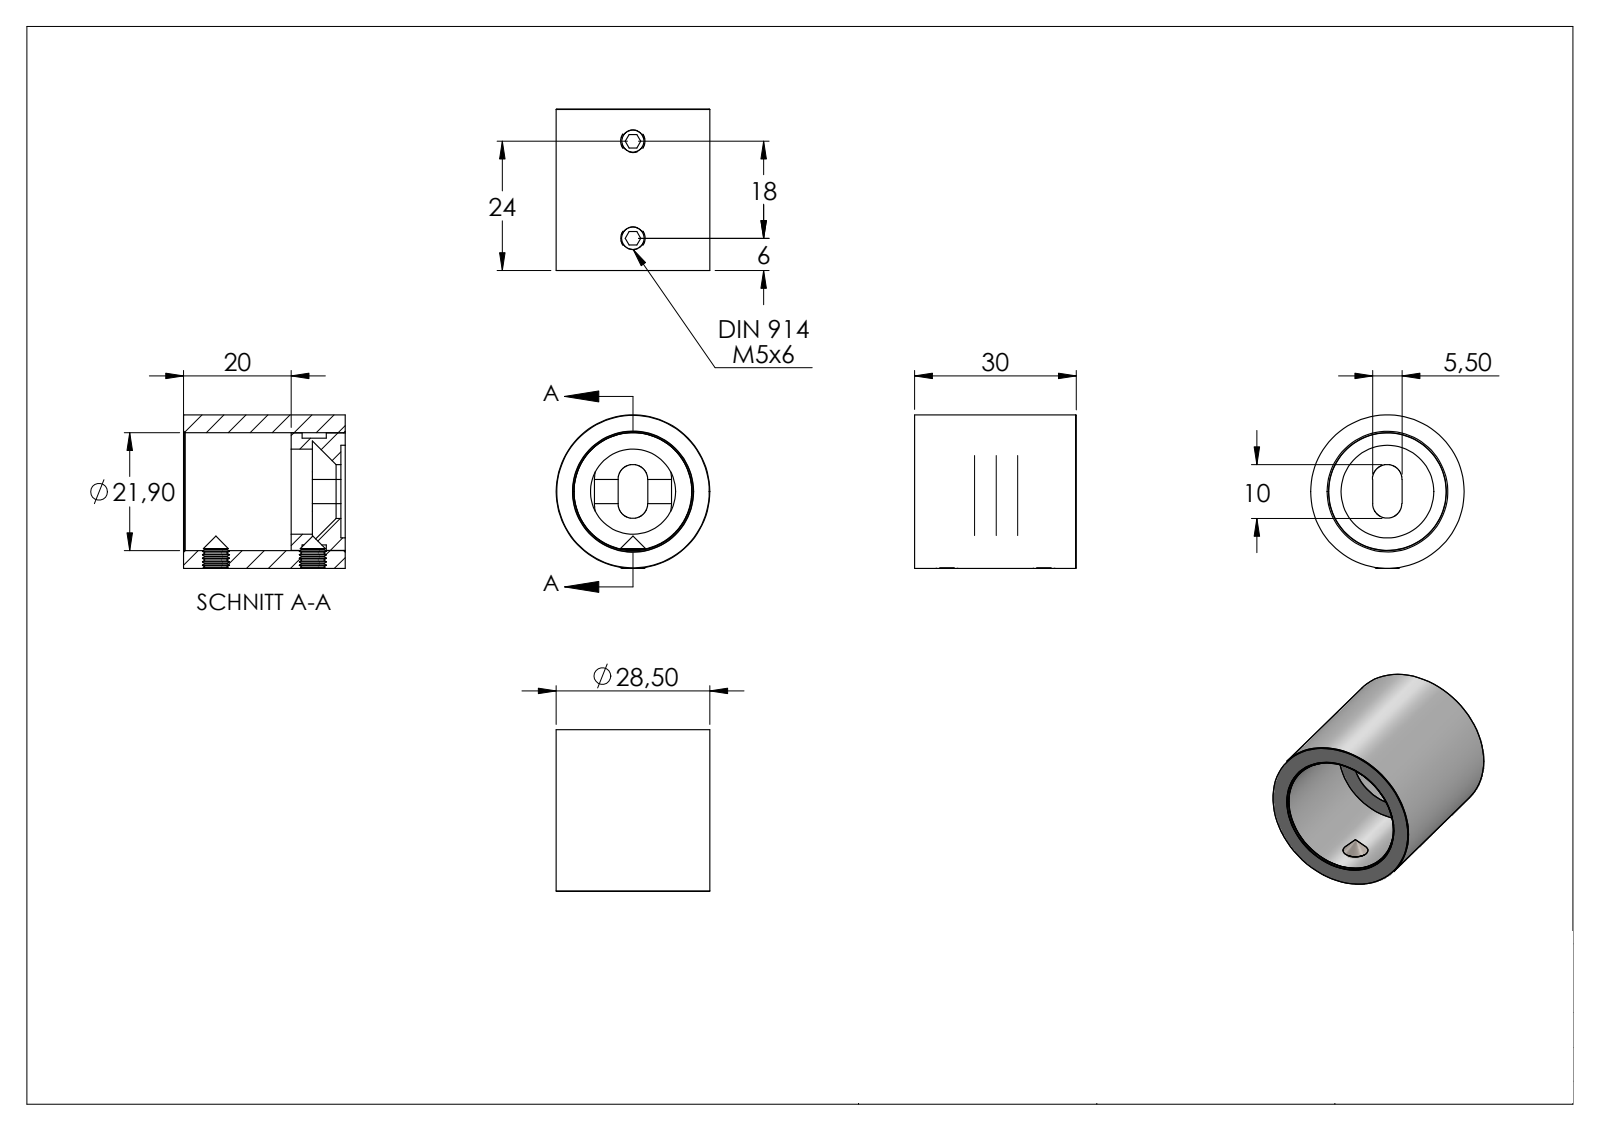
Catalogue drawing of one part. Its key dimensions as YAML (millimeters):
part_name: "54180-240-XX Teil1; 54180-240-XX Teil1_54180-V4A-21 Teil1; 54180-240-XX Teil2; 54180-240-XX Teil2_54180-V4A-21 Teil2 (+3 more)"
step_written_by: "SolidWorks 2018 (CONFIG_CONTROL_DESIGN)"
units: millimeters
bodies: {solids: 4, faces: 379, planar: 185, cylindrical: 51, other: 143}
overall_size: [30, 28.5, 28.5]
volume: 9741
surface_area: 7443
round_holes:
  - {diameter: 4.2, count: 2}
  - {diameter: 15.8, count: 1}
  - {diameter: 17.2, count: 1}
  - {diameter: 21.9, count: 1}
round_bosses_or_shafts:
  - {diameter: 5, count: 2}
  - {diameter: 28.5, count: 1}
  - {diameter: 21.8, count: 1}
  - {diameter: 19.8, count: 1}
partial_cylinders:
  - {radius: 2.75, count: 2}
  - {radius: 10.95, count: 1}
face_to_face_distances: [30, 0.8, 29.2, 10, 9.2, 20, 6.5, 2.7, 8, 7.2]
hole_center_spacings: [18]
